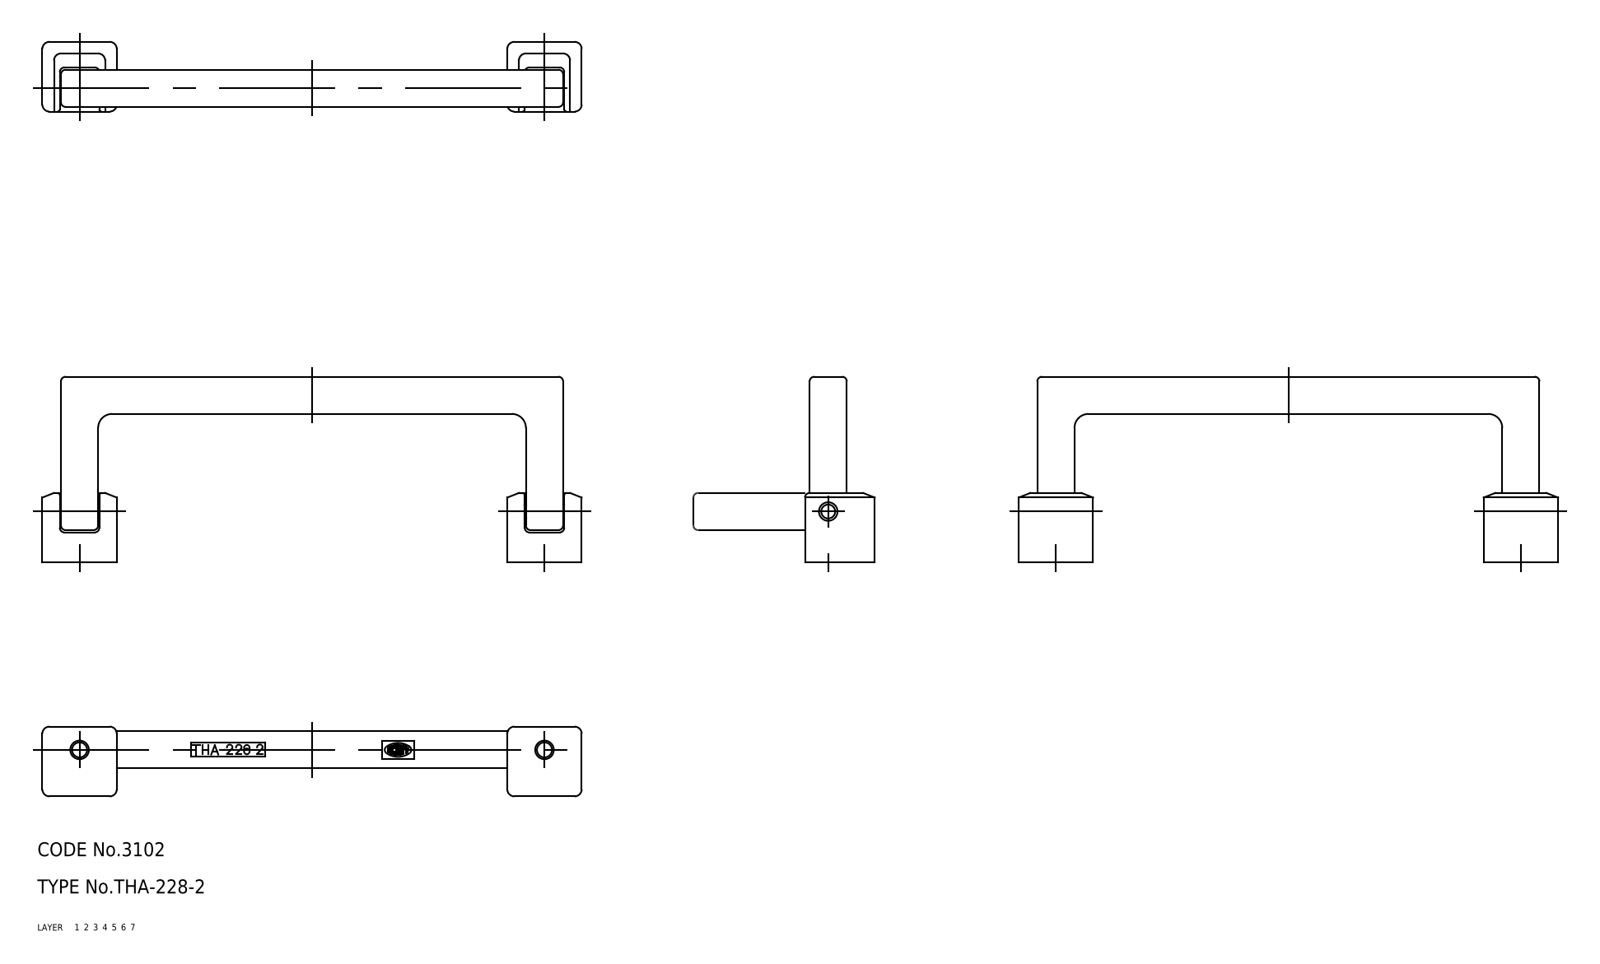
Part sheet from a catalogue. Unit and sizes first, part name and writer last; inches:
Units: inches
Overall size (bounding box): 4.567 × 1.575 × 0.591
Volume: 0.933 in³ · Surface area: 13.23 in²
Bodies: 5 solids, 176 faces (0 planar, 0 cylindrical, 176 other)
Part name (STEP PRODUCT): pin; base; pull; THA_228_2_24910_36
STEP written by: CADfix (AUTOMOTIVE_DESIGN)
